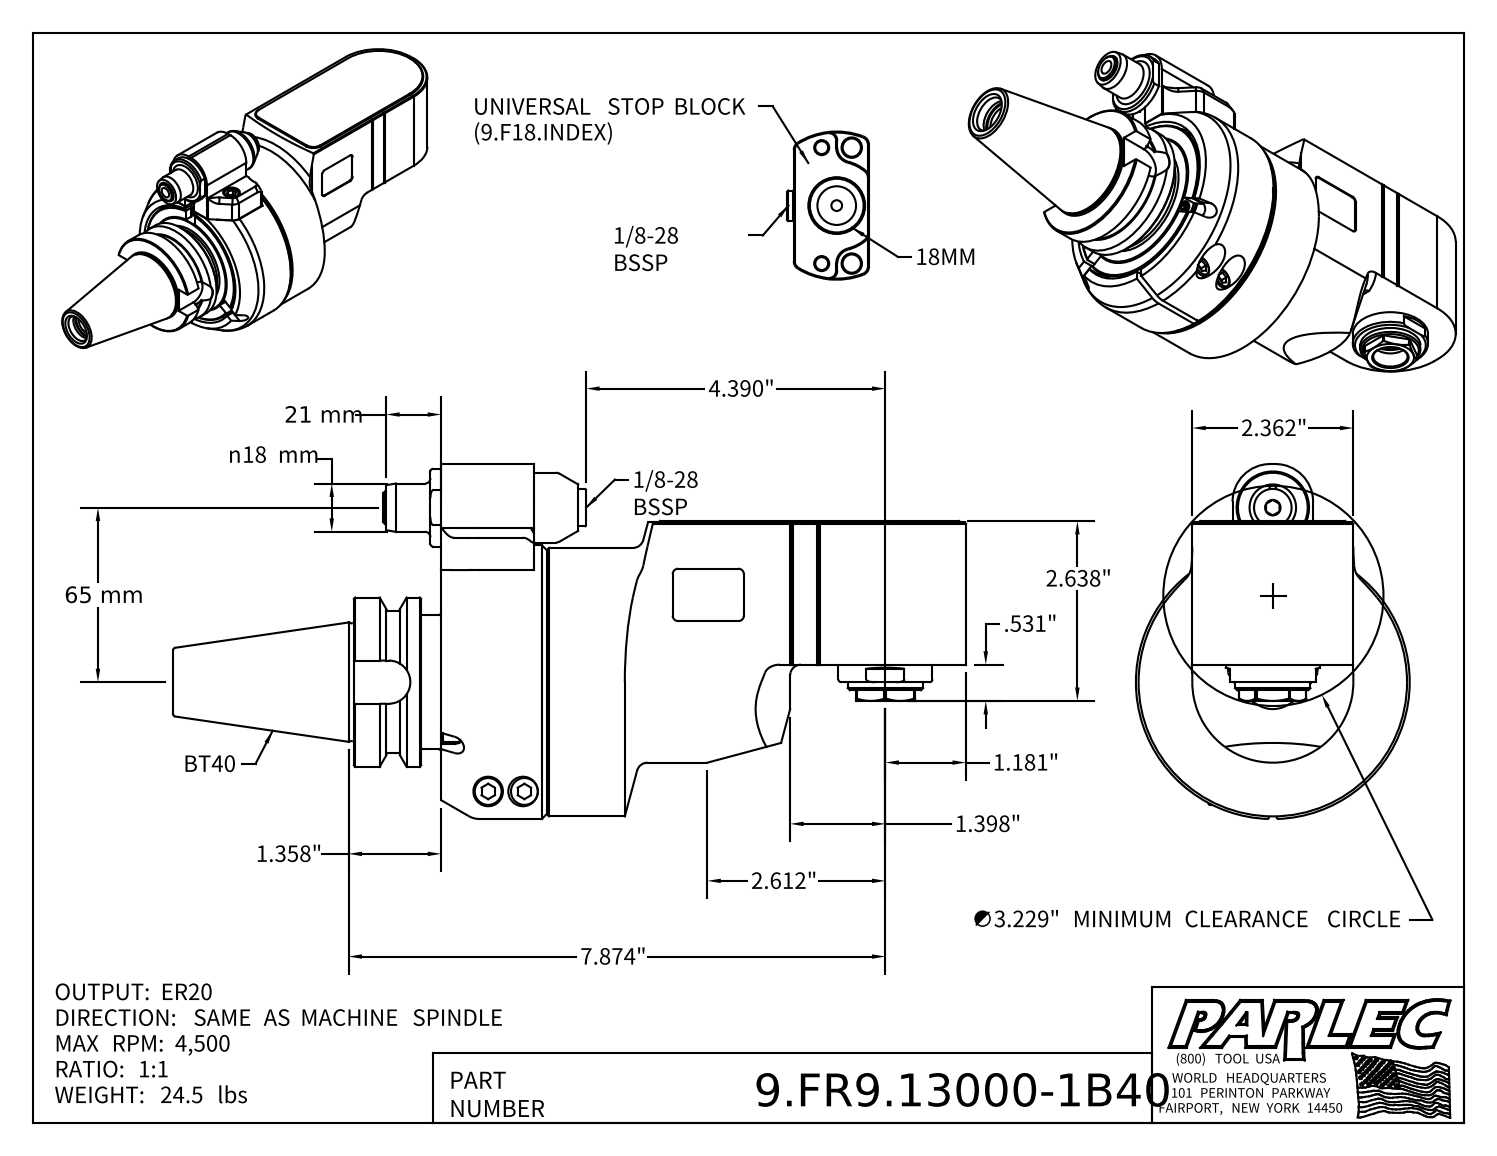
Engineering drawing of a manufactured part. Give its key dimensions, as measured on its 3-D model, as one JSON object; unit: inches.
{"part_name": "9.FR9.13000-1B40; 9_FR9_13000; 9_GA1_346_2 (EVO, Type 1, BT40, 65mm)", "step_written_by": "Autodesk Inventor 2022 (AUTOMOTIVE_DESIGN)", "units": "inches", "bodies": {"solids": 5, "faces": 438, "planar": 217, "cylindrical": 106, "other": 115}, "overall_size": [11.63, 5.206, 4.016], "volume_in3": 73.3, "surface_area_in2": 234.7, "round_holes": [[0.102, 2], [0.165, 2], [0.197, 2], [0.409, 2], [0.433, 2], [0.098, 1], [0.118, 1], [0.157, 1], [0.256, 1], [0.276, 1], [0.472, 1], [0.492, 1]], "round_bosses_or_shafts": [[0.394, 4], [0.236, 4], [0.709, 2], [4.016, 1], [3.937, 1], [3.74, 1], [3.031, 1], [2.48, 1]], "partial_cylinders_radius": [[0.157, 5], [0.079, 4], [0.02, 2], [0.039, 2], [0.138, 2], [0.197, 2], [0.551, 2], [1.142, 2]], "face_to_face_distances": [1.22, 2.362, 0.039, 1.555, 0.02, 0.295, 0.719, 1.26, 0.276, 0.335], "hole_center_spacings": [0.276, 0.049, 0.512, 0.551, 1.72, 2.283, 2.559, 2.835]}
